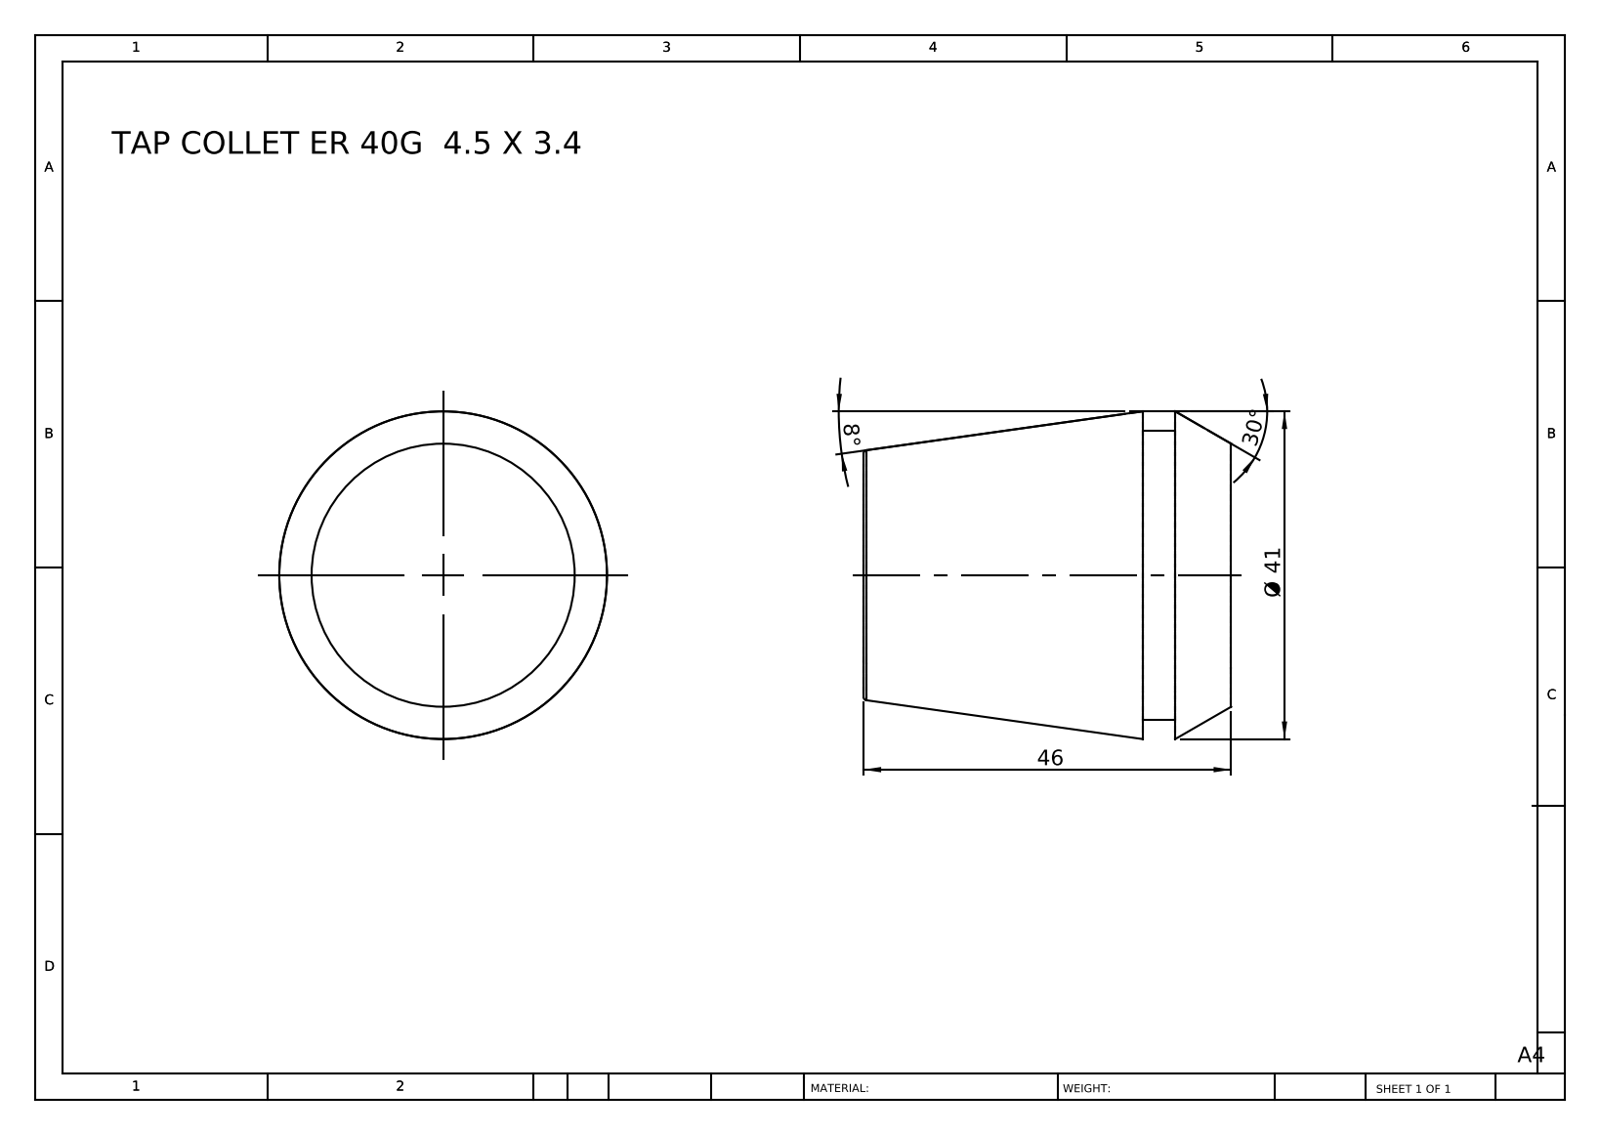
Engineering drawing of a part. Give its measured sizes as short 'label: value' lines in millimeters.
name: TAP COLLET ER 40G 4.5 X 3.4
written by: SolidWorks 2014 (CONFIG_CONTROL_DESIGN)
unit: mm
bodies: 1 solid, 12 faces (4 planar, 2 cylindrical, 6 other)
size: 46 × 41 × 41
volume: 47 690 mm³; area: 7 586 mm²
bosses: 1× ⌀36.2
face distances: 46, 11.1, 34.9, 7, 4.1, 39
